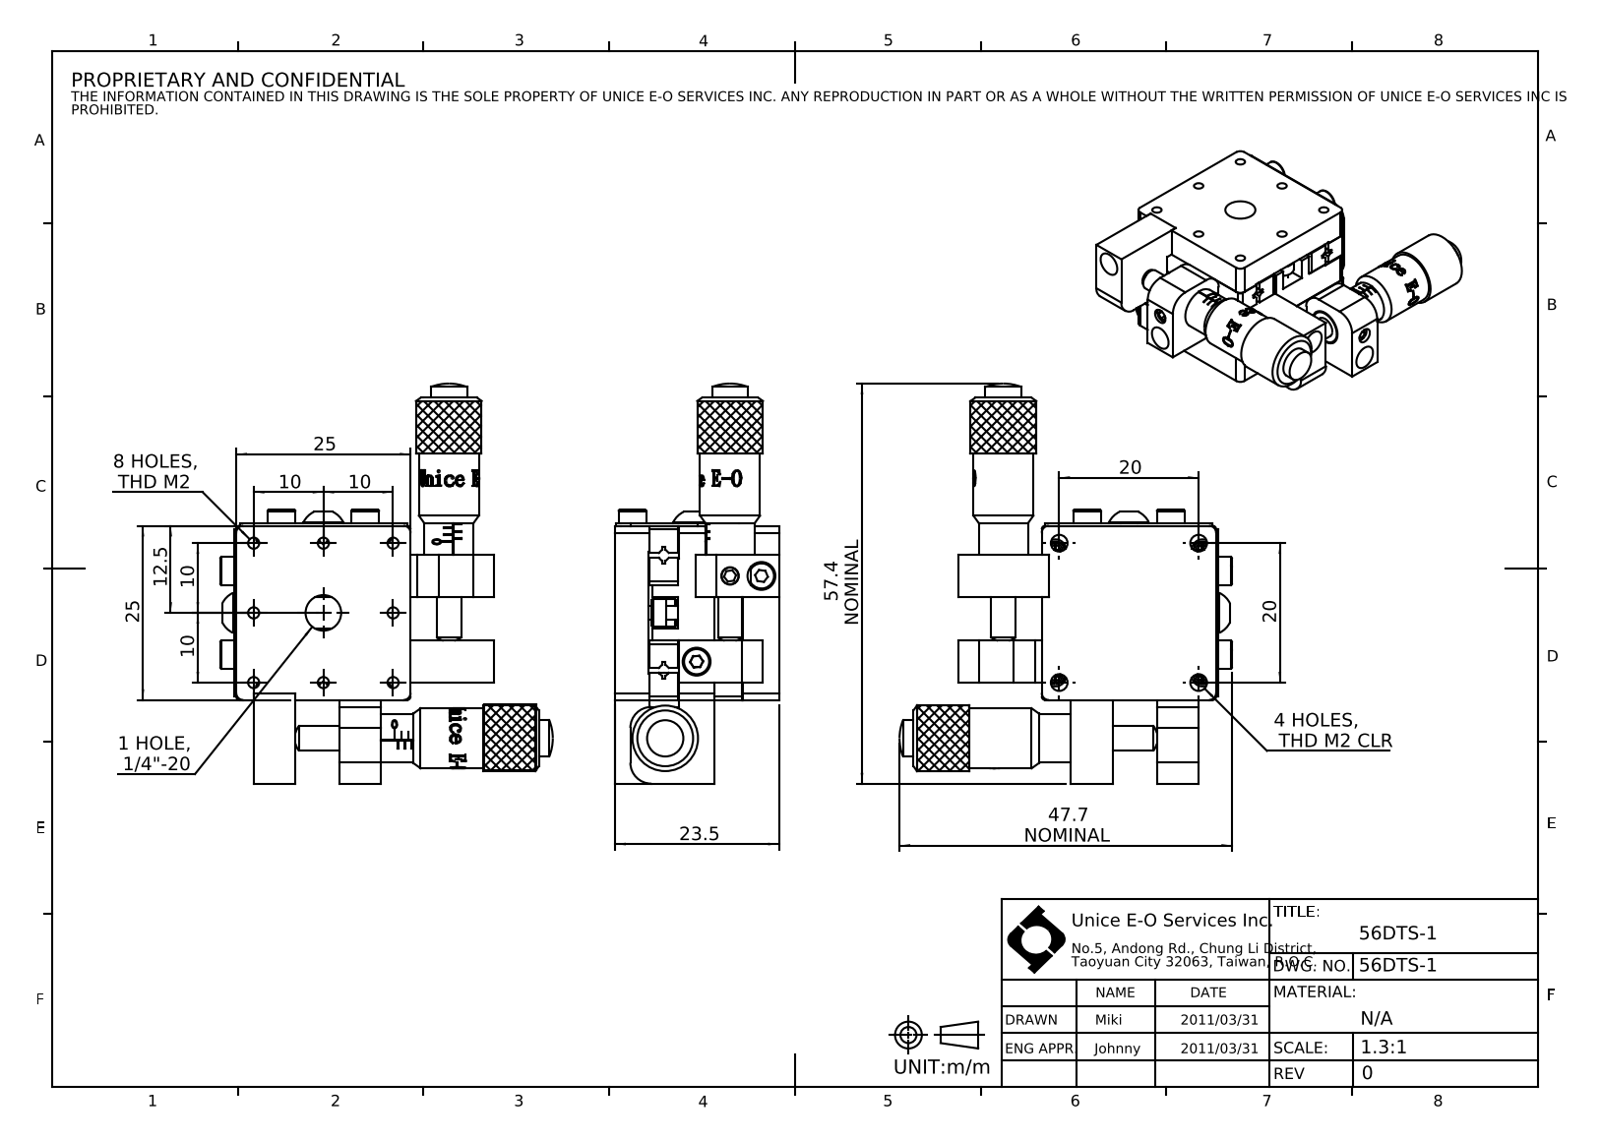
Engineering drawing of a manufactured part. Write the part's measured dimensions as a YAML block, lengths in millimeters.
part_name: "56DTS-1"
step_written_by: "SolidWorks 2016 (CONFIG_CONTROL_DESIGN)"
units: millimeters
bodies: {solids: 65, faces: 2441, planar: 1181, cylindrical: 680, other: 580}
overall_size: [57.4, 47.7, 23.5]
volume: 18365
surface_area: 21587
round_holes:
  - {diameter: 1.25, count: 24}
  - {diameter: 1.8, count: 24}
  - {diameter: 3.1, count: 24}
  - {diameter: 1.6, count: 16}
  - {diameter: 2.4, count: 8}
  - {diameter: 1.2, count: 4}
  - {diameter: 2.2, count: 4}
  - {diameter: 2.5, count: 4}
  - {diameter: 4.4, count: 4}
  - {diameter: 4, count: 3}
  - {diameter: 3, count: 2}
  - {diameter: 3.5, count: 2}
round_bosses_or_shafts:
  - {diameter: 2.5, count: 24}
  - {diameter: 1.4, count: 24}
  - {diameter: 2, count: 12}
  - {diameter: 4, count: 9}
  - {diameter: 5.7, count: 4}
  - {diameter: 3, count: 4}
  - {diameter: 9.4, count: 2}
  - {diameter: 8.6, count: 2}
partial_cylinders:
  - {radius: 0.1, count: 96}
  - {radius: 0.5, count: 12}
  - {radius: 2, count: 8}
  - {radius: 3, count: 8}
  - {radius: 1, count: 4}
  - {radius: 1.8, count: 4}
  - {radius: 4.28, count: 2}
face_to_face_distances: [9.2, 4.2, 9, 16.5, 5, 4, 8.5, 25, 14.5, 4.8]
hole_center_spacings: [9, 10.11, 18.79, 14.92, 4.6, 16.5, 18, 4.17]
